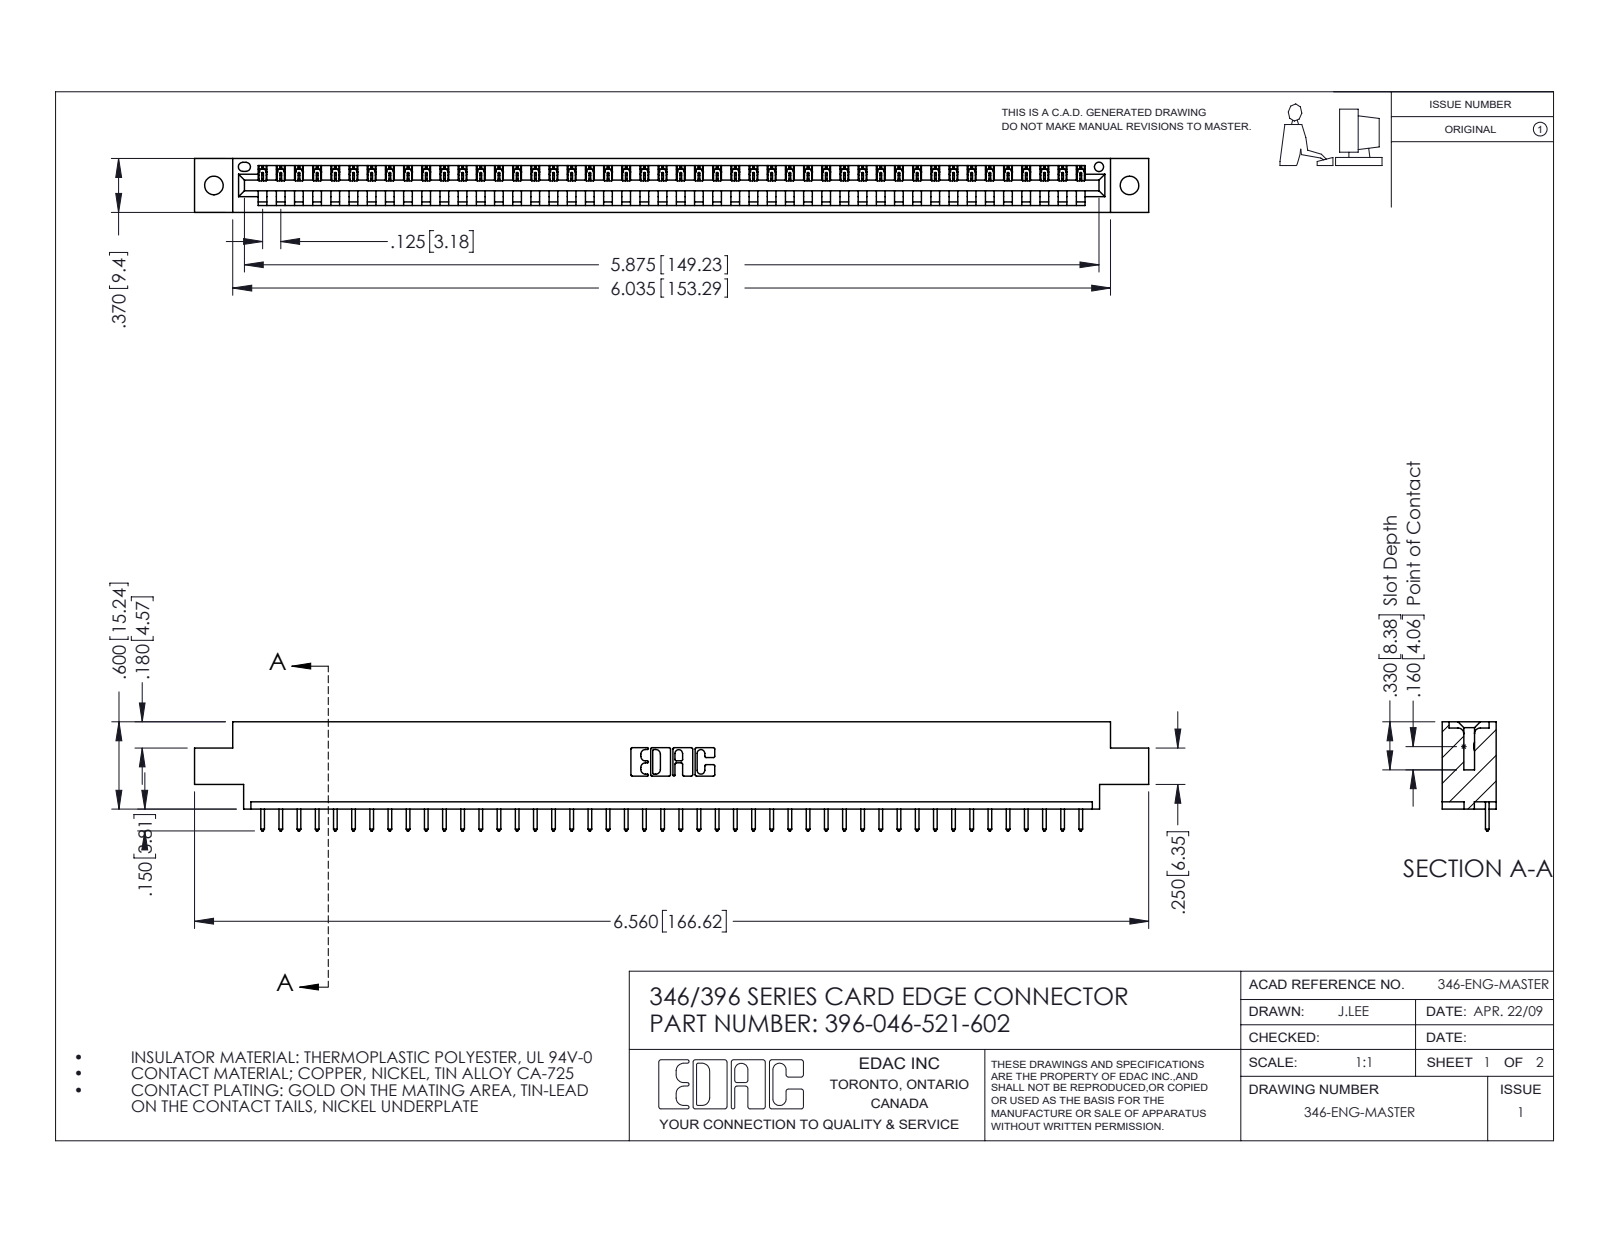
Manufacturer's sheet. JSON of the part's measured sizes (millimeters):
{"part_name": "396-046-521-602; 345-292-001_345-293-121; 346 Part_0.170 Offset - 0.128 Dia", "step_written_by": "SolidWorks 2016 (CONFIG_CONTROL_DESIGN)", "units": "millimeters", "bodies": {"solids": 47, "faces": 2794, "planar": 1920, "cylindrical": 874, "other": 0}, "overall_size": [166.6, 19.1, 9.4], "volume_mm3": 15600, "surface_area_mm2": 18980, "round_holes": [[3.3, 2], [1.6, 1]], "partial_cylinders_radius": [[0.2, 92], [0.3, 92], [0.3, 22], [0.2, 6], [0.8, 6], [0.7, 3], [0.8, 2], [1, 2]], "face_to_face_distances": [1.2, 8.2, 9.4, 6.4, 1.8, 7.6, 0.6, 3.8, 5.6, 2.5], "hole_center_spacings": [6.2, 154.6, 159.9]}
